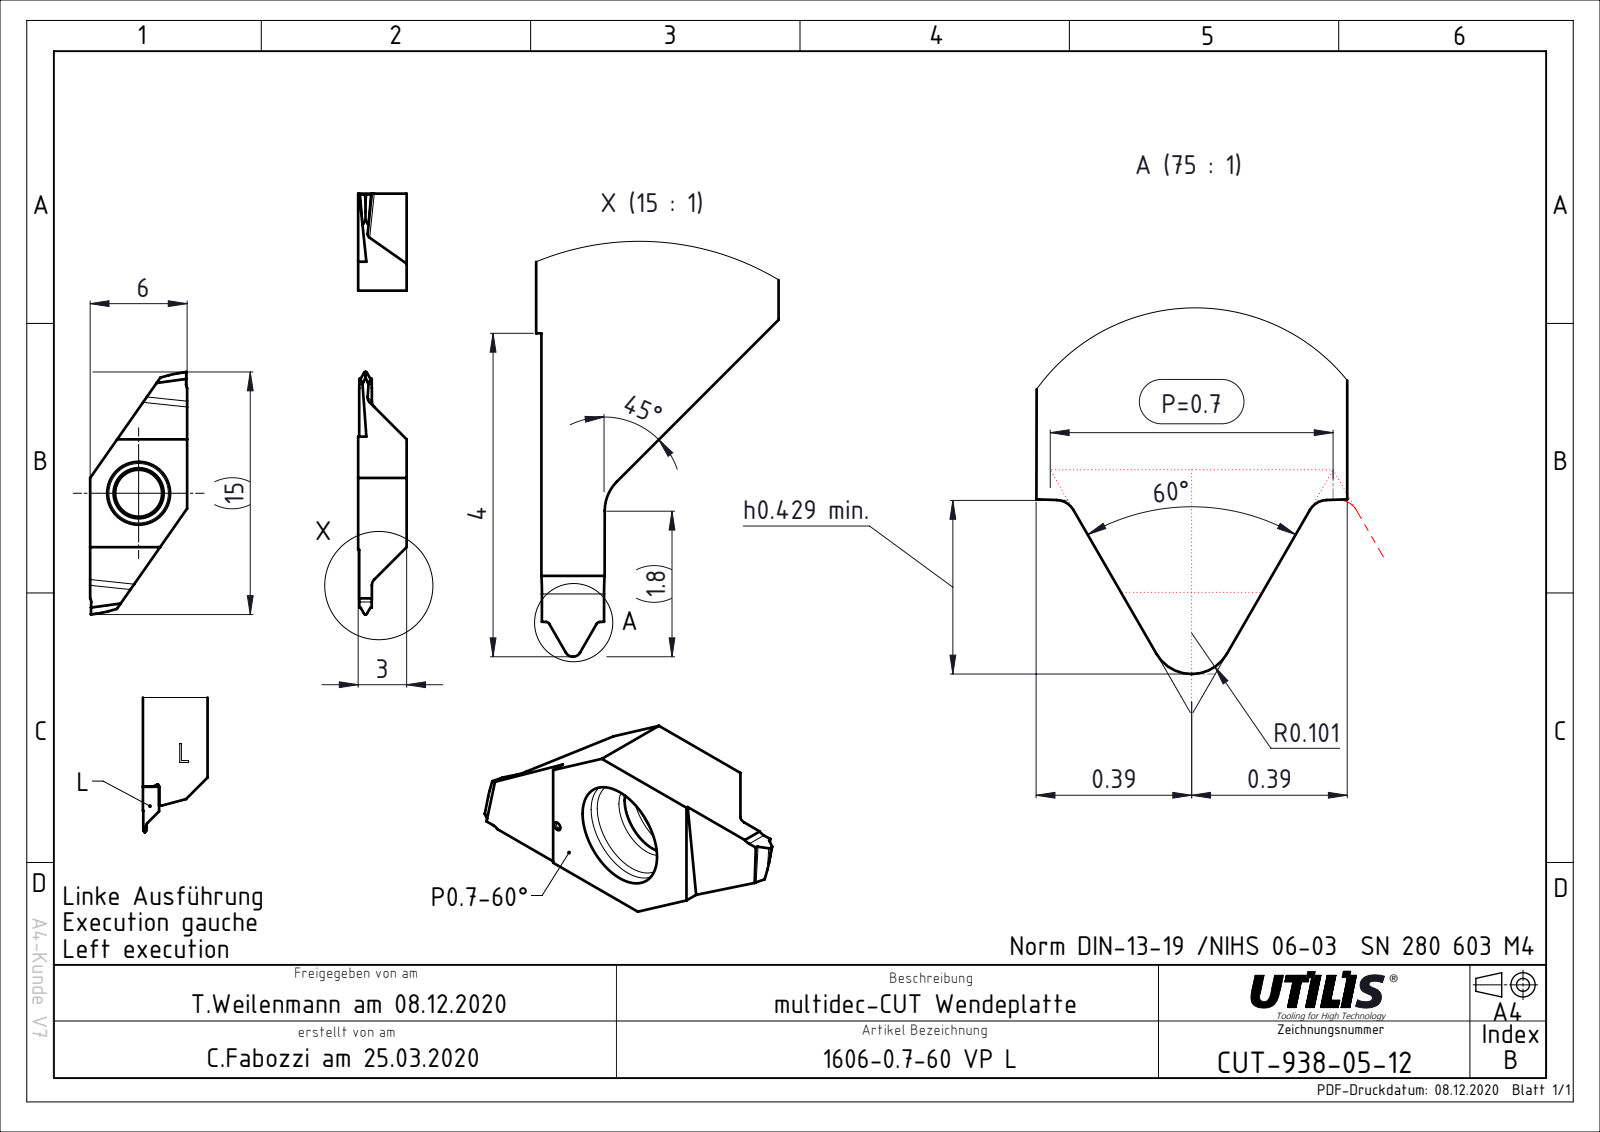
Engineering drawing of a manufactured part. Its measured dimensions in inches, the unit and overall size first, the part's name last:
Units: inches
Overall size (bounding box): 0.591 × 0.236 × 0.118
Round holes (diameter × count): ⌀0.114 ×1
Partial cylindrical surfaces — rounded edges, fillets, slot ends (radius × count): R0.004 ×4, R0.02 ×2
Main face-to-face distances: 0.236, 0.118, 0.024, 0.441, 0.354, 0.472, 0.276, 0.499
Volume: 0.008 in³ · Surface area: 0.324 in²
Bodies: 1 solid, 42 faces (24 planar, 14 cylindrical, 4 other)
Part name (STEP PRODUCT): CUT-938-05; ASME Y14.5
STEP written by: FormatWorks Professional (AP242_MANAGED_MODEL_BASED_3D_ENGINEERING_MIM_LF)
